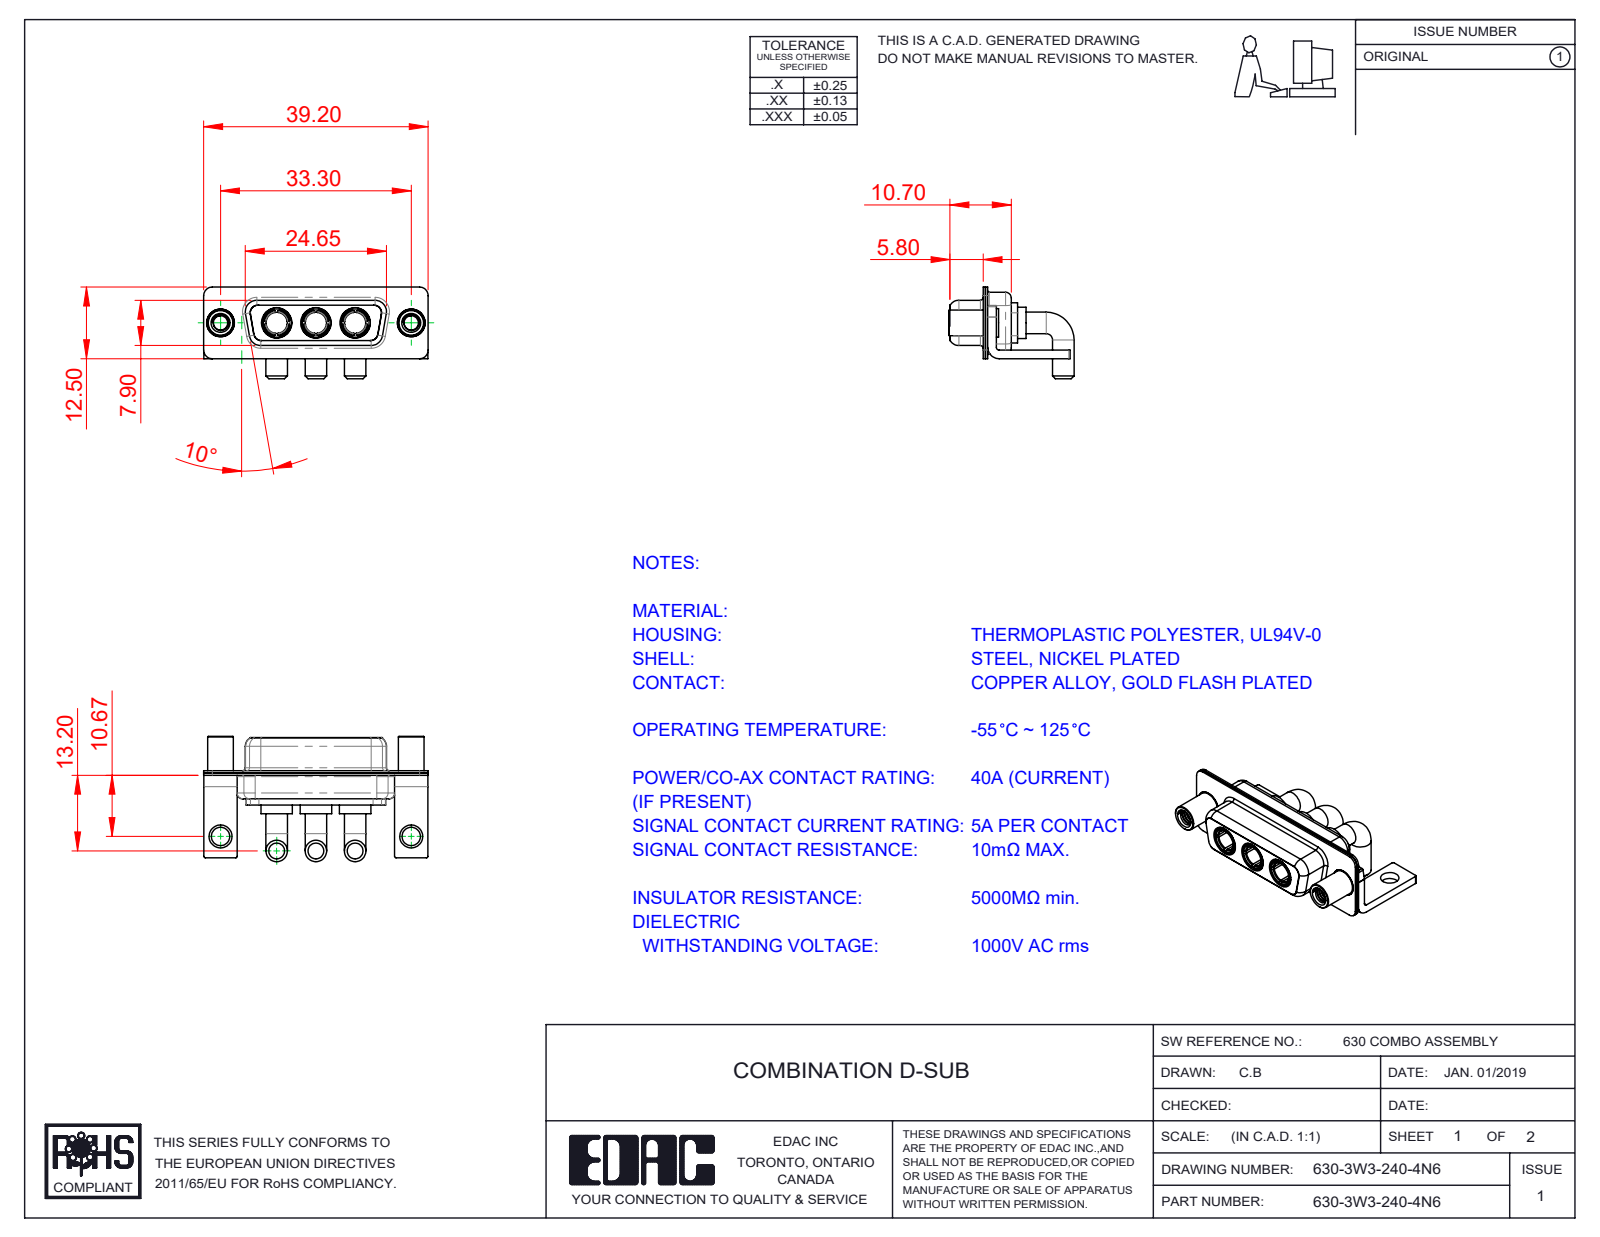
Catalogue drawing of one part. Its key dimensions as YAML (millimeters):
part_name: "630Combo Shell Rear_15 Contacts; 630-3W3-240-4N6; 630Combo Housing_3W3; Power Socket_40A RA (+3 more)"
step_written_by: "SolidWorks 2020 (CONFIG_CONTROL_DESIGN)"
units: millimeters
bodies: {solids: 13, faces: 611, planar: 176, cylindrical: 284, other: 151}
overall_size: [39.2, 21.88, 16]
volume: 3244
surface_area: 6980
round_holes:
  - {diameter: 4.85, count: 5}
  - {diameter: 3.7, count: 3}
  - {diameter: 5.3, count: 3}
  - {diameter: 2.5, count: 2}
  - {diameter: 3.2, count: 2}
  - {diameter: 4, count: 2}
  - {diameter: 4.05, count: 2}
round_bosses_or_shafts:
  - {diameter: 3.75, count: 6}
  - {diameter: 5.5, count: 3}
  - {diameter: 5.2, count: 3}
  - {diameter: 4.96, count: 3}
  - {diameter: 4.75, count: 3}
  - {diameter: 5, count: 2}
  - {diameter: 4.95, count: 2}
  - {diameter: 4.8, count: 2}
partial_cylinders:
  - {radius: 0.25, count: 16}
  - {radius: 1.5, count: 16}
  - {radius: 2, count: 13}
  - {radius: 1.35, count: 12}
  - {radius: 1.6, count: 8}
  - {radius: 0.5, count: 5}
  - {radius: 0.6, count: 4}
  - {radius: 0.65, count: 4}
face_to_face_distances: [0.4, 0.8, 1.4, 0.45, 1.5, 8.45, 1.8, 8.9, 6.2, 7.05]
hole_center_spacings: [6.85, 9.8, 16.65, 23.5, 33.3, 13.7]
